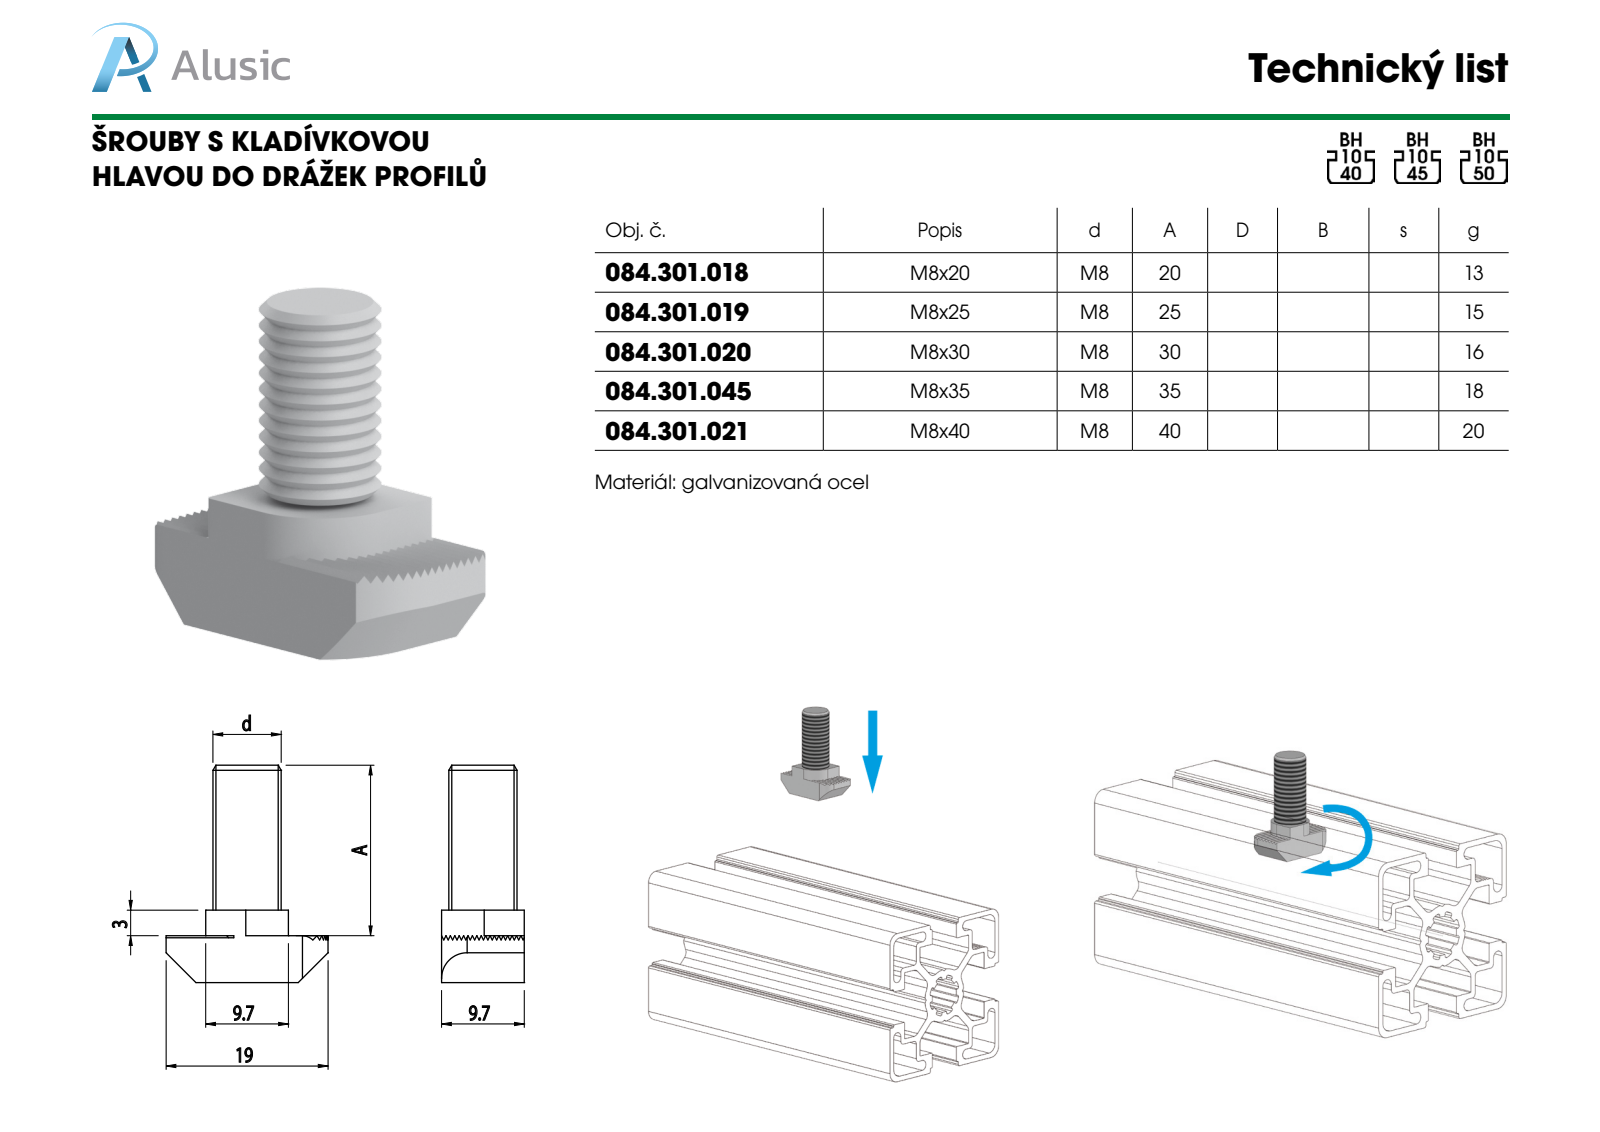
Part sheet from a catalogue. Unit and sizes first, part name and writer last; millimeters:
Units: millimetres
Overall size (bounding box): 40.5 × 19 × 9.8
Round bosses / shafts (diameter × count): ⌀8 ×1
Partial cylindrical surfaces — rounded edges, fillets, slot ends (radius × count): R3 ×2, R5 ×2
Main face-to-face distances: 9.8, 0.46, 0.92, 6.44, 0.44, 6.9, 0.48, 1.38, 5.98, 40.5
Volume: 2 729 mm³ · Surface area: 1 657 mm²
Bodies: 1 solid, 169 faces (143 planar, 24 cylindrical, 2 other)
Part name (STEP PRODUCT): 084.301.045
STEP written by: SolidWorks 2012 (CONFIG_CONTROL_DESIGN)
